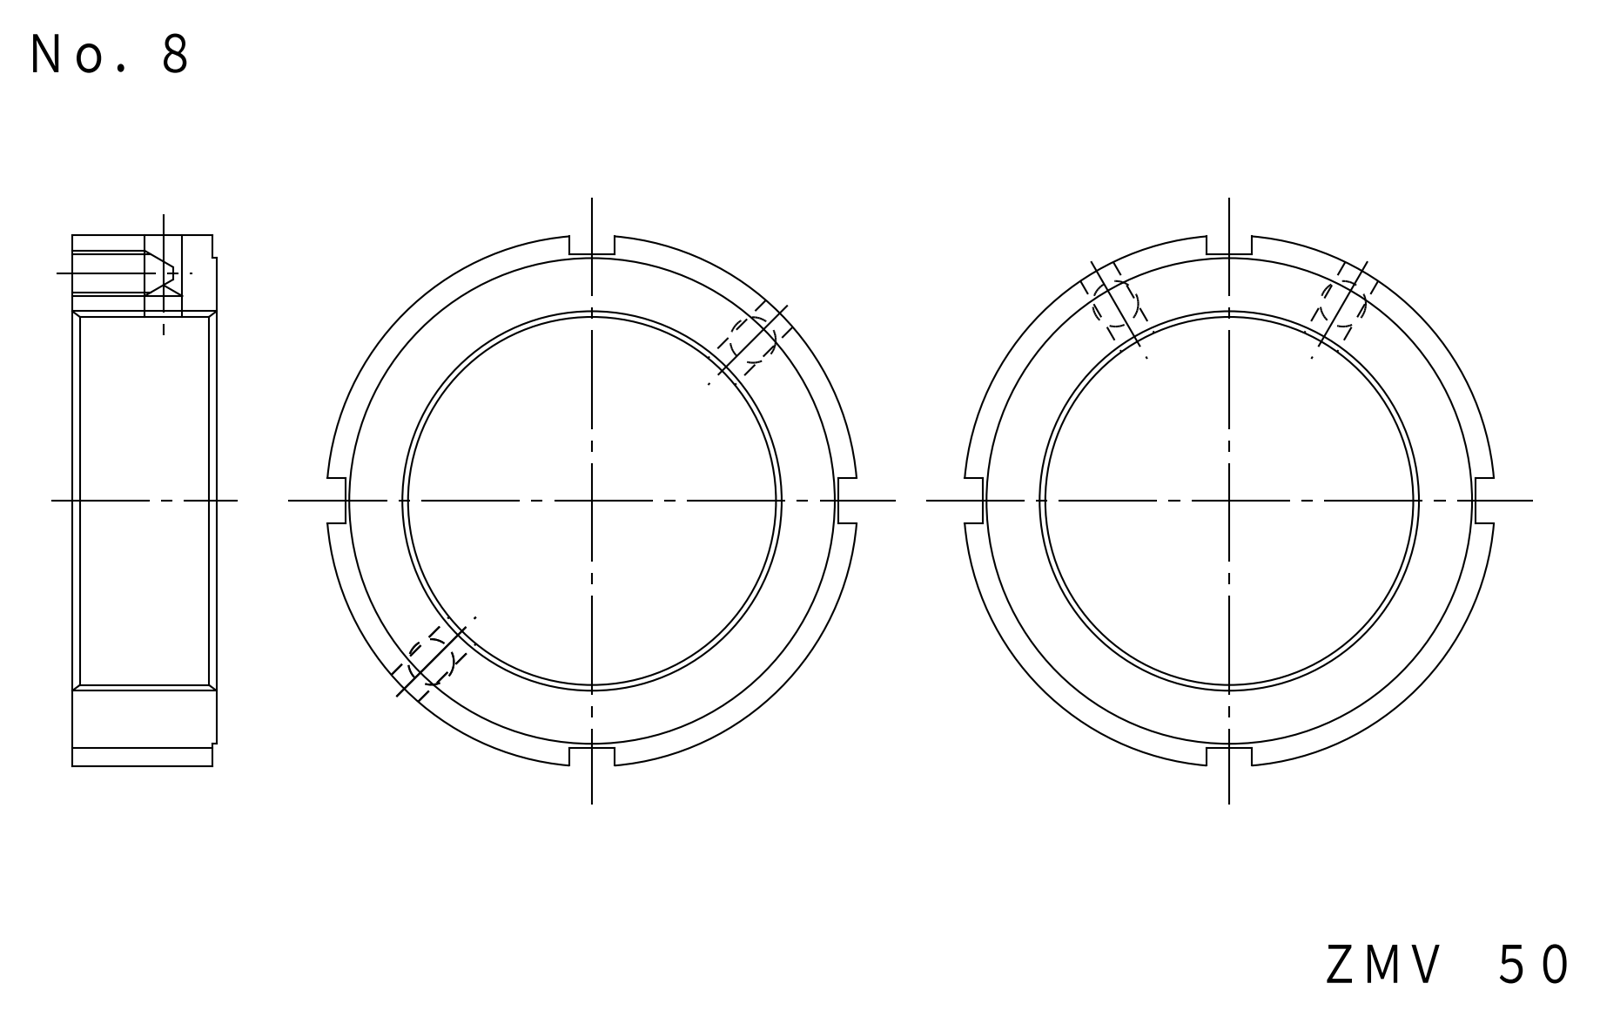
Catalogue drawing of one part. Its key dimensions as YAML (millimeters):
part_name: "FKD ZMV50"
step_written_by: "Autodesk Inventor LT (CONFIG_CONTROL_DESIGN)"
units: millimeters
bodies: {solids: 1, faces: 25, planar: 15, cylindrical: 10, other: 0}
overall_size: [69.74, 69.74, 19]
volume: 33640
surface_area: 11626
round_holes:
  - {diameter: 4.92, count: 2}
  - {diameter: 5, count: 2}
  - {diameter: 50, count: 1}
round_bosses_or_shafts:
  - {diameter: 70, count: 1}
  - {diameter: 64, count: 1}
face_to_face_distances: [19, 0.5, 18.5, 29.5, 35.5, 65, 6]
hole_center_spacings: [30, 59.99]
